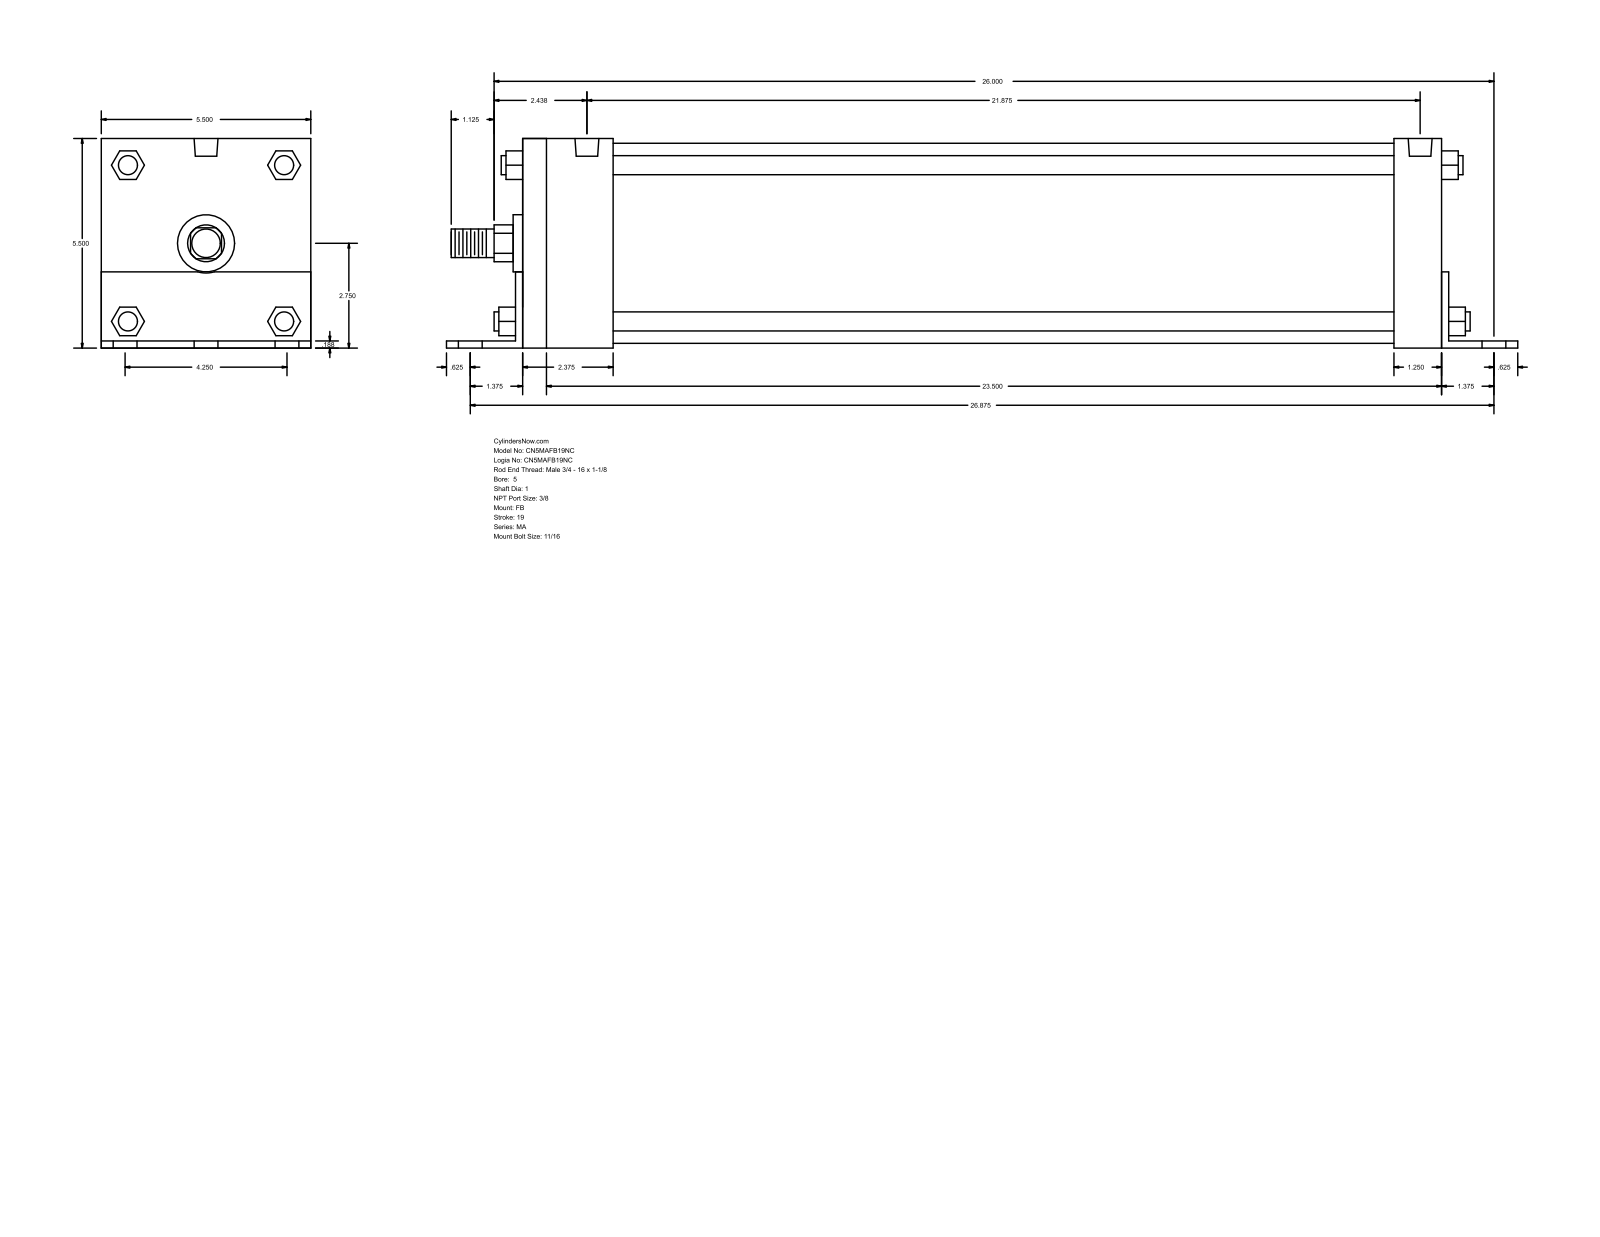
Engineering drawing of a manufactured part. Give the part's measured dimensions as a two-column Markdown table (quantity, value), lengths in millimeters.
| quantity | value |
| --- | --- |
| part name | MA_FB__0500_1 |
| STEP written by | GSSL Pune (CONFIG_CONTROL_DESIGN) |
| units | millimeters |
| bodies | 0 solids, 140 faces (105 planar, 35 cylindrical, 0 other) |
| overall size | 714.38 × 139.75 × 139.7 |
| round holes (diameter × count) | 17.46 × 6, 11.11 × 4, 15.93 × 2 |
| round bosses / shafts (diameter × count) | 12.7 × 4, 133.35 × 1, 38.1 × 1, 25.4 × 1, 19.05 × 1 |
| partial cylindrical surfaces (radius × count) | 12.29 × 1, 19.81 × 1 |
| main face-to-face distances | 139.7, 4.76, 139.75, 617.54, 4.71, 134.99, 612.78, 622.3, 36.51, 31.75 |
| hole center spacings | 53.98, 684.76, 682.63, 73.04, 76.34, 94.68, 98.63, 107.96 |
